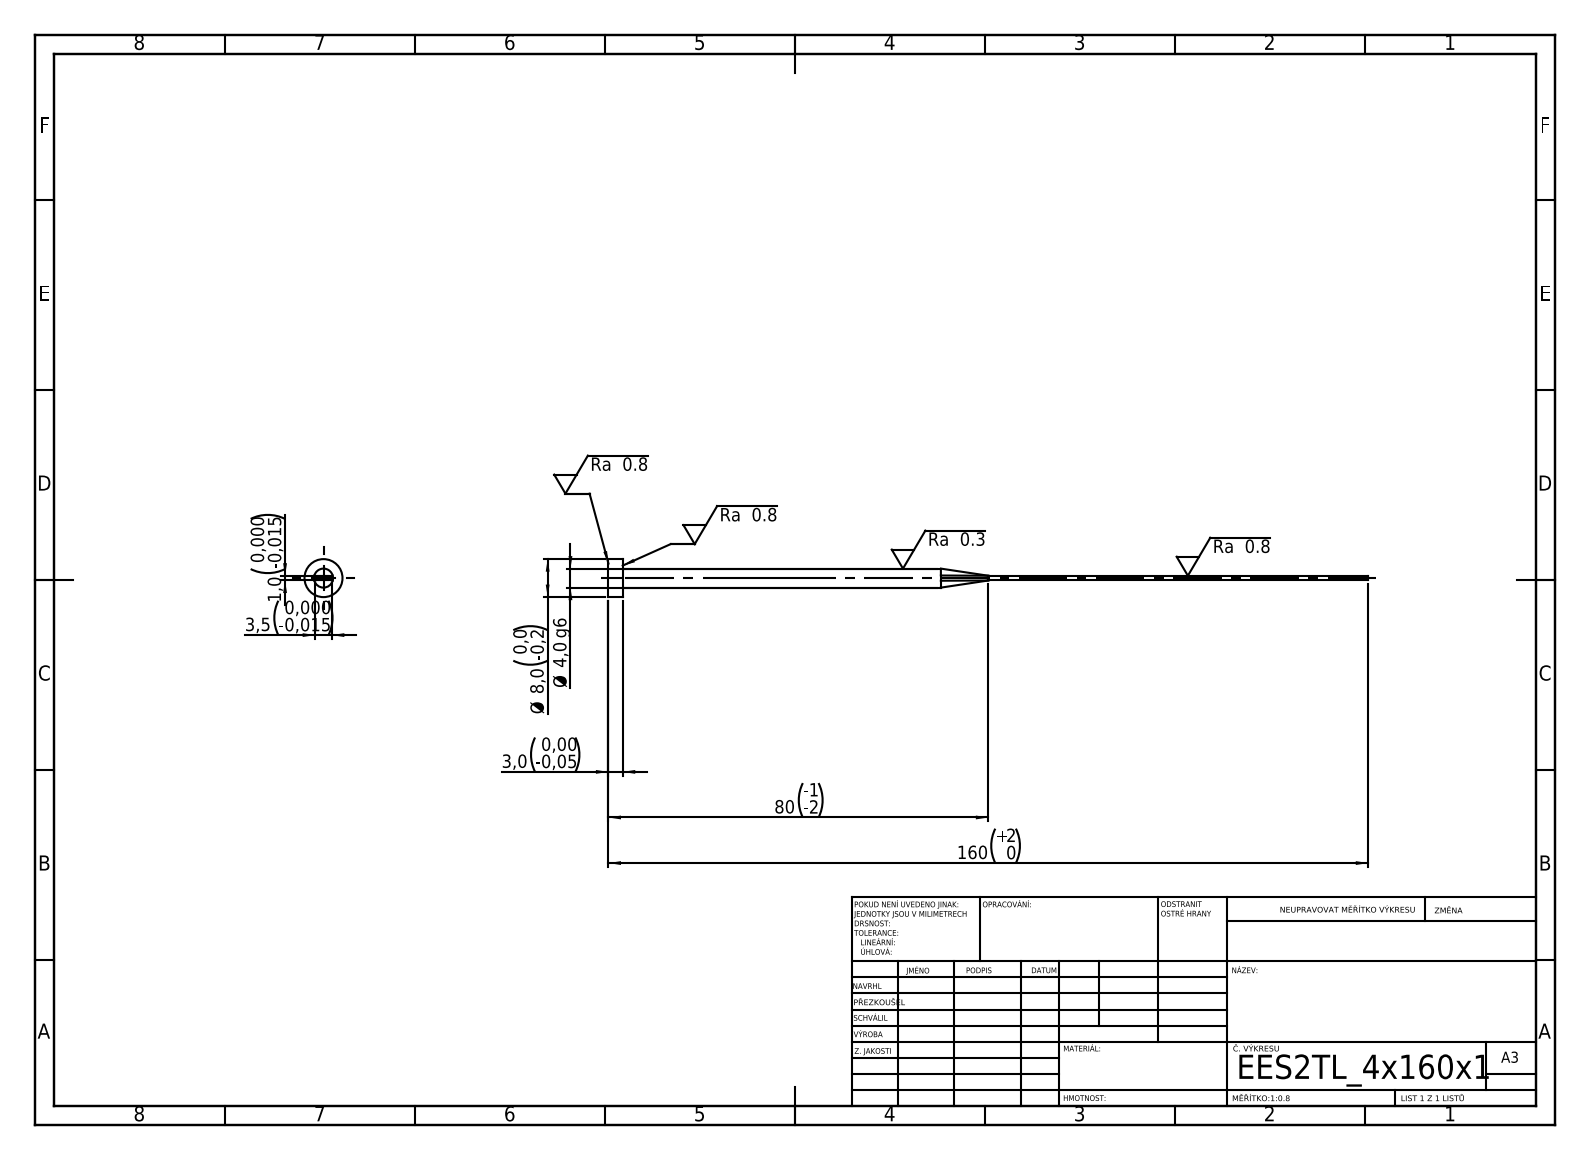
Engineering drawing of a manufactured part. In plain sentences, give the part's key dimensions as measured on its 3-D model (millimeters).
Its 3-D file was written by "SolidWorks 2019 (CONFIG_CONTROL_DESIGN)". It is 1 solid with 15 faces: 7 planar, 4 cylindrical and 4 other. Overall it measures 160 by 8 by 8 millimeters. Its volume is 1 350 cubic millimeters and its surface area 1 833 square millimeters. Round bosses or shafts: 1 of diameter 8, 1 of diameter 4. The main face-to-face distances are 1, 3.5, 3, 160, 157.
